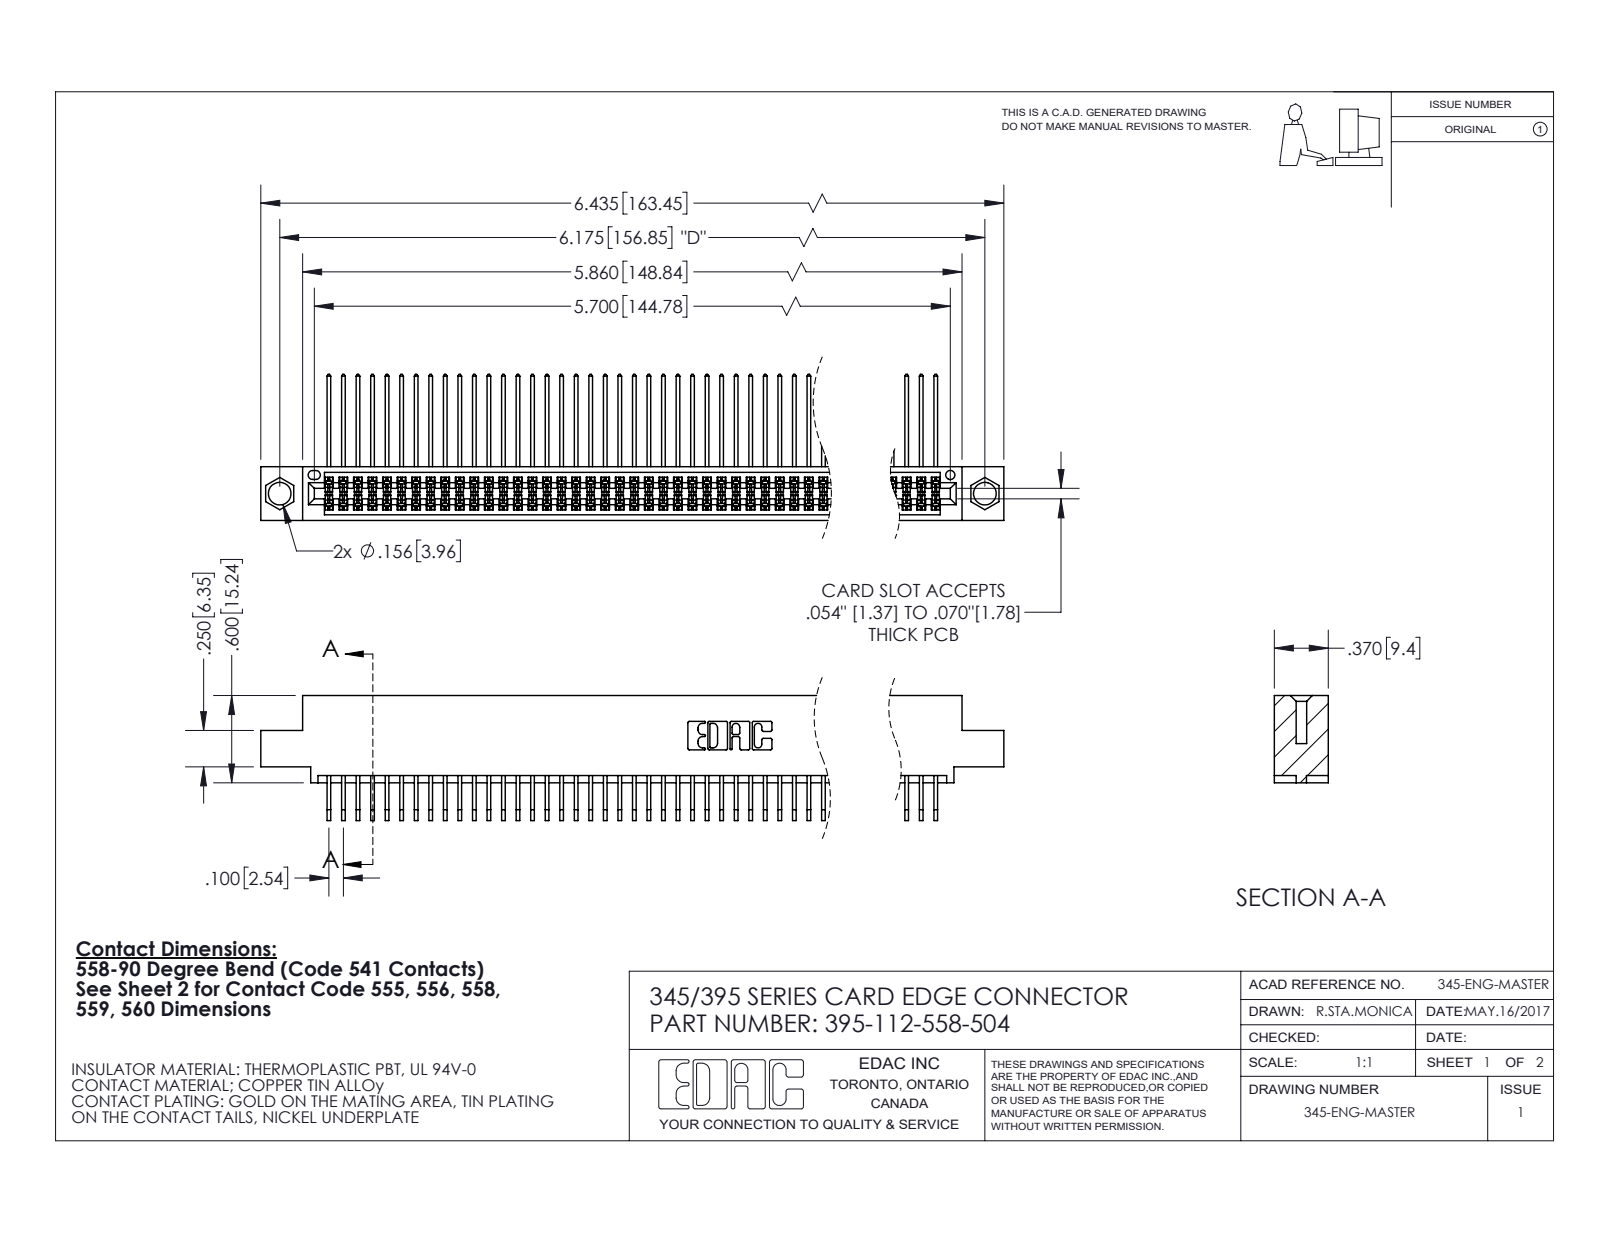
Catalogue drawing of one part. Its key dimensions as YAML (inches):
part_name: "345-292-001_558 559 Tail - 1; 345-292-001_558 Tail - 2; 345 Part_0.110 Offset - 0.156 Dia-TI; 395-112-558-504"
step_written_by: "SolidWorks 2020 (CONFIG_CONTROL_DESIGN)"
units: inches
bodies: {solids: 113, faces: 5968, planar: 4018, cylindrical: 1950, other: 0}
overall_size: [6.435, 1.005, 0.859]
volume: 1.005
surface_area: 42.79
round_holes:
  - {diameter: 0.156, count: 2}
  - {diameter: 0.064, count: 1}
partial_cylinders:
  - {radius: 0.006, count: 224}
  - {radius: 0.01, count: 22}
  - {radius: 0.007, count: 6}
  - {radius: 0.031, count: 6}
  - {radius: 0.026, count: 3}
  - {radius: 0.014, count: 2}
  - {radius: 0.019, count: 2}
  - {radius: 0.022, count: 2}
face_to_face_distances: [0.072, 0.298, 0.2, 0.37, 0.098, 0.272, 0.025, 0.225, 0.025, 0.175]
hole_center_spacings: [0.27, 5.939, 6.175]
